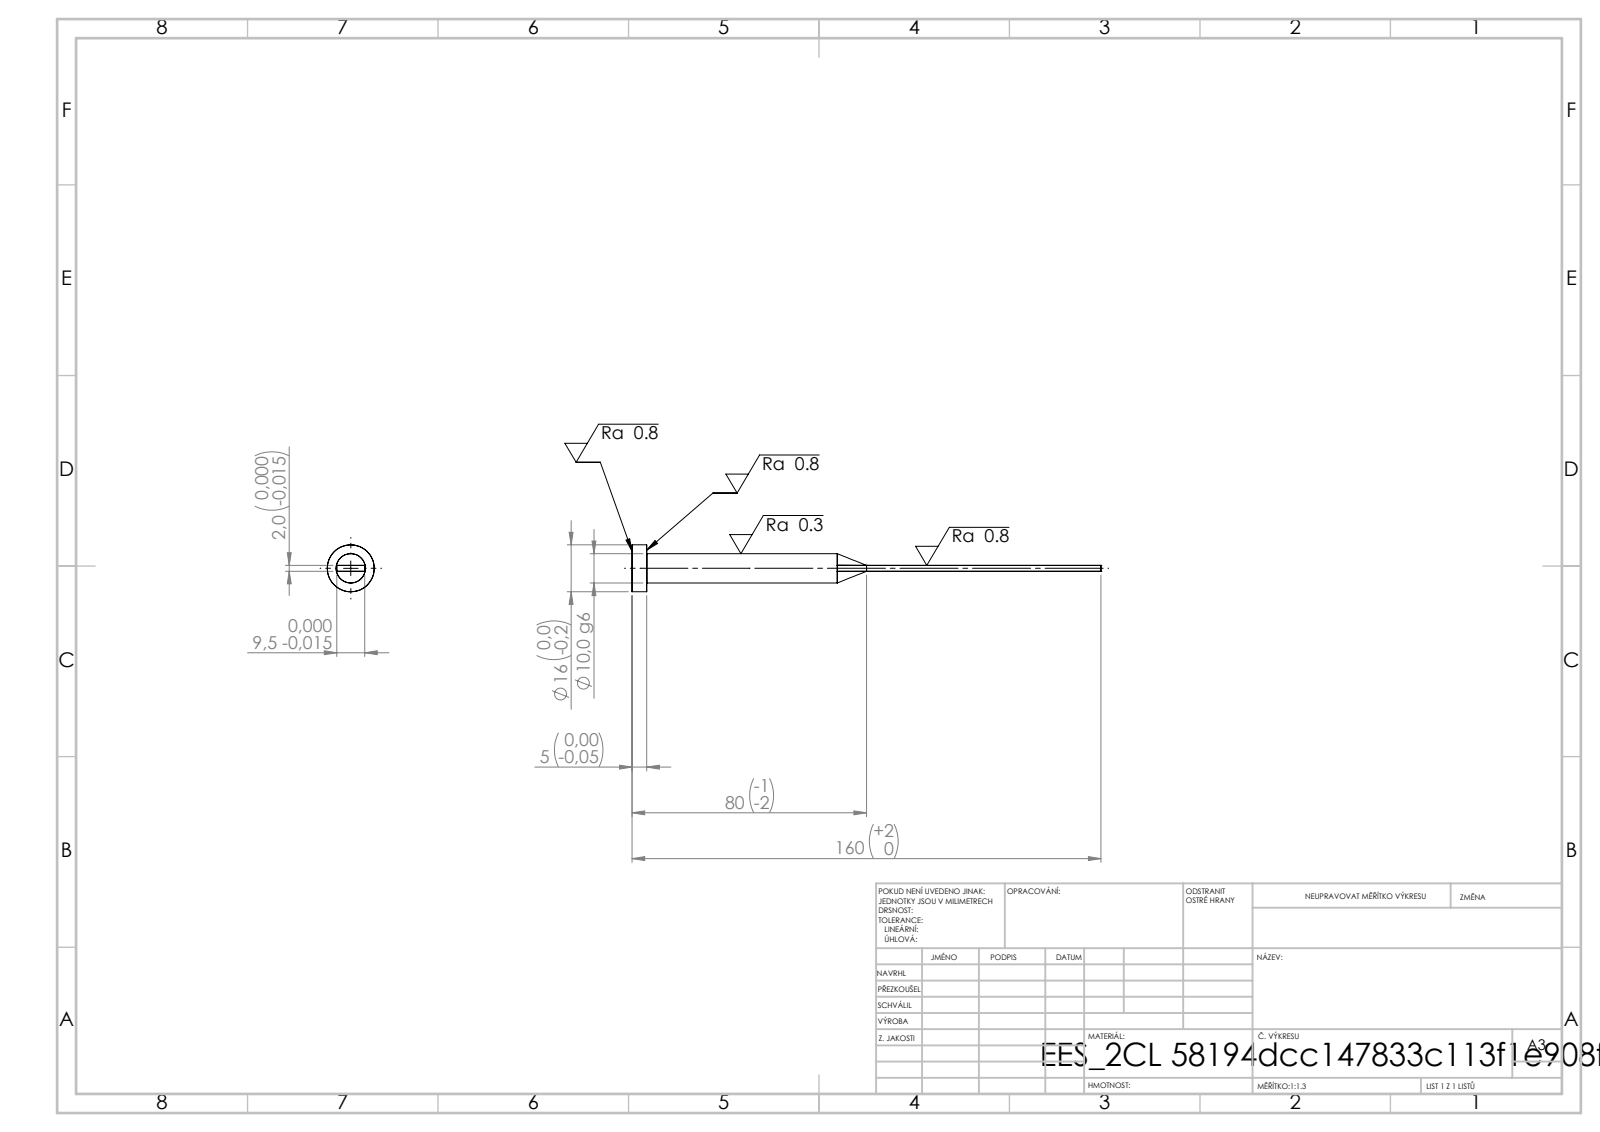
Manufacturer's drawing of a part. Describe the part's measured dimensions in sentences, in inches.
Its 3-D file was written by "SolidWorks 2019 (CONFIG_CONTROL_DESIGN)". It is 1 solid with 15 faces: 7 planar, 4 cylindrical and 4 other. Overall it measures 6.299 by 0.63 by 0.63 inches. Its volume is 0.494 cubic inches and its surface area 7.355 square inches. Round bosses or shafts: 1 of diameter 0.63, 1 of diameter 0.394. The main face-to-face distances are 0.079, 0.374, 0.197, 6.299, 6.102.
